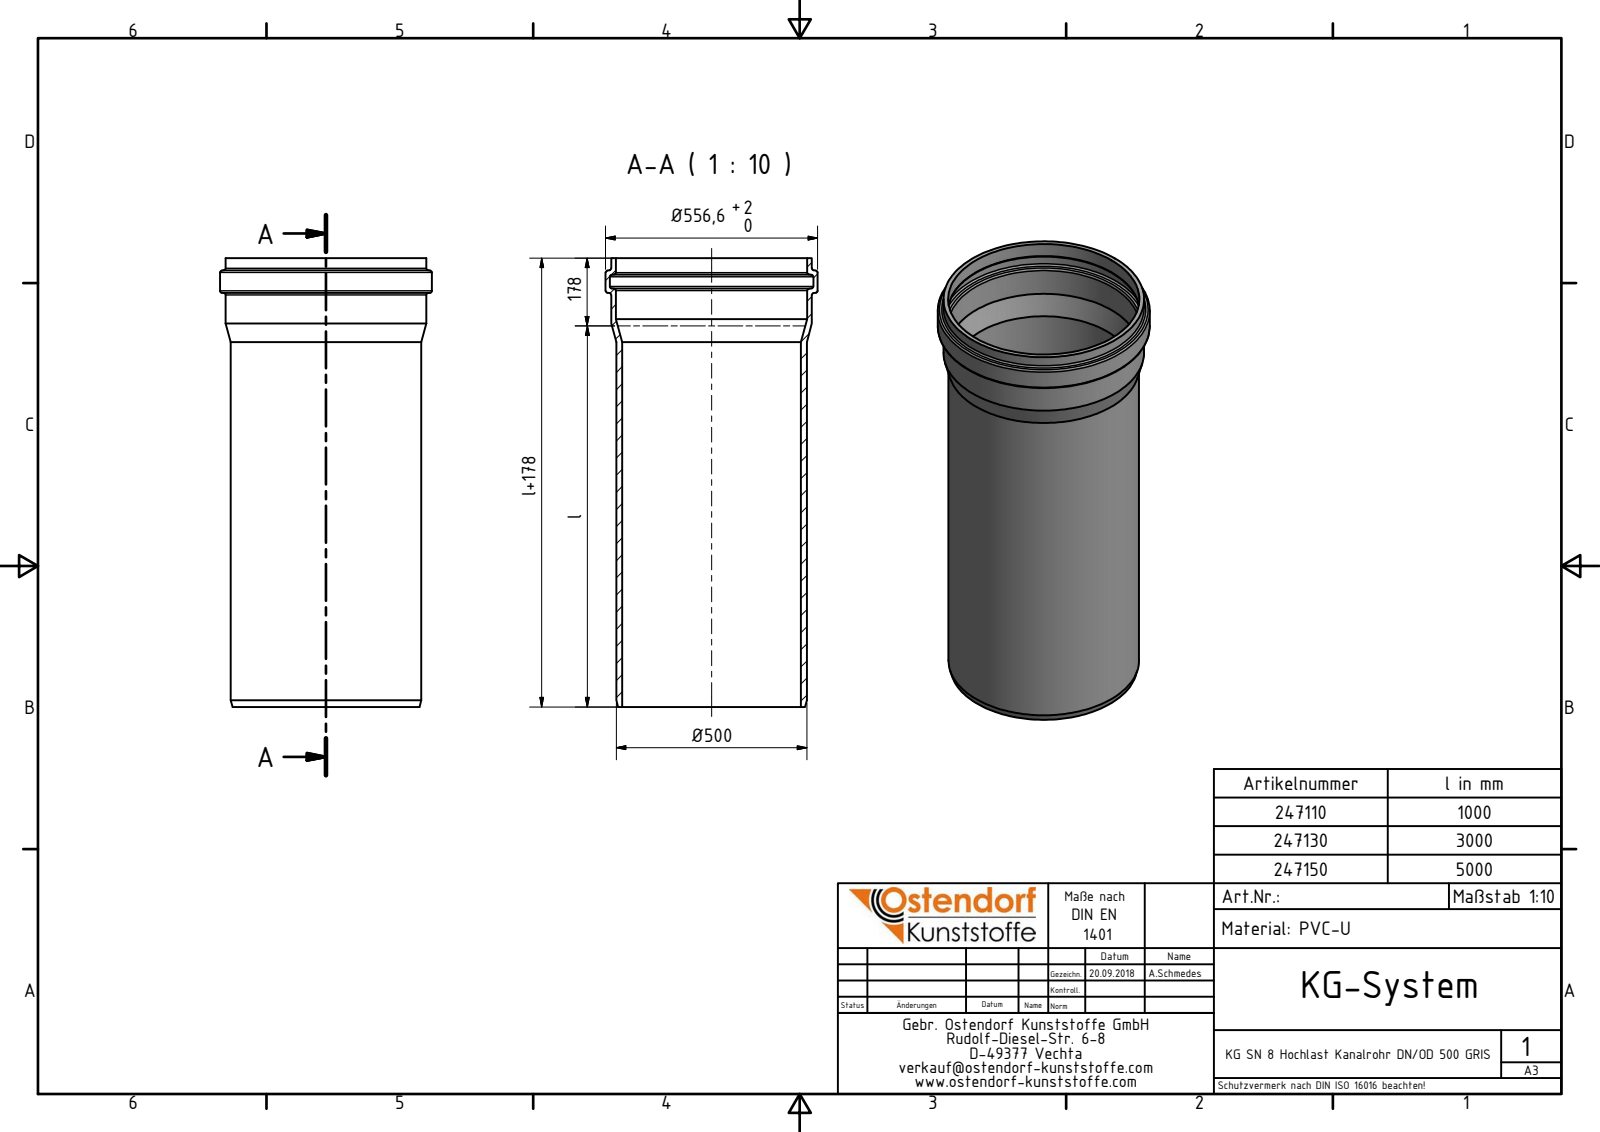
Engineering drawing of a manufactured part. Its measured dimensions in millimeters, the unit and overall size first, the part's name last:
Units: millimetres
Overall size (bounding box): 5178 × 556.6 × 556.6
Round holes (diameter × count): ⌀469.5 ×1, ⌀502 ×1, ⌀534.6 ×1
Round bosses / shafts (diameter × count): ⌀556.6 ×1, ⌀526.8 ×1, ⌀500.5 ×1
Main face-to-face distances: 5178
Volume: 122 200 000 mm³ · Surface area: 15 940 000 mm²
Bodies: 1 solid, 25 faces (2 planar, 8 cylindrical, 15 other)
Part name (STEP PRODUCT): 247150 KGEM Passlängen SN 8 DN_OD 500x5000 GRIS
STEP written by: Autodesk Inventor 2016 (AUTOMOTIVE_DESIGN)
